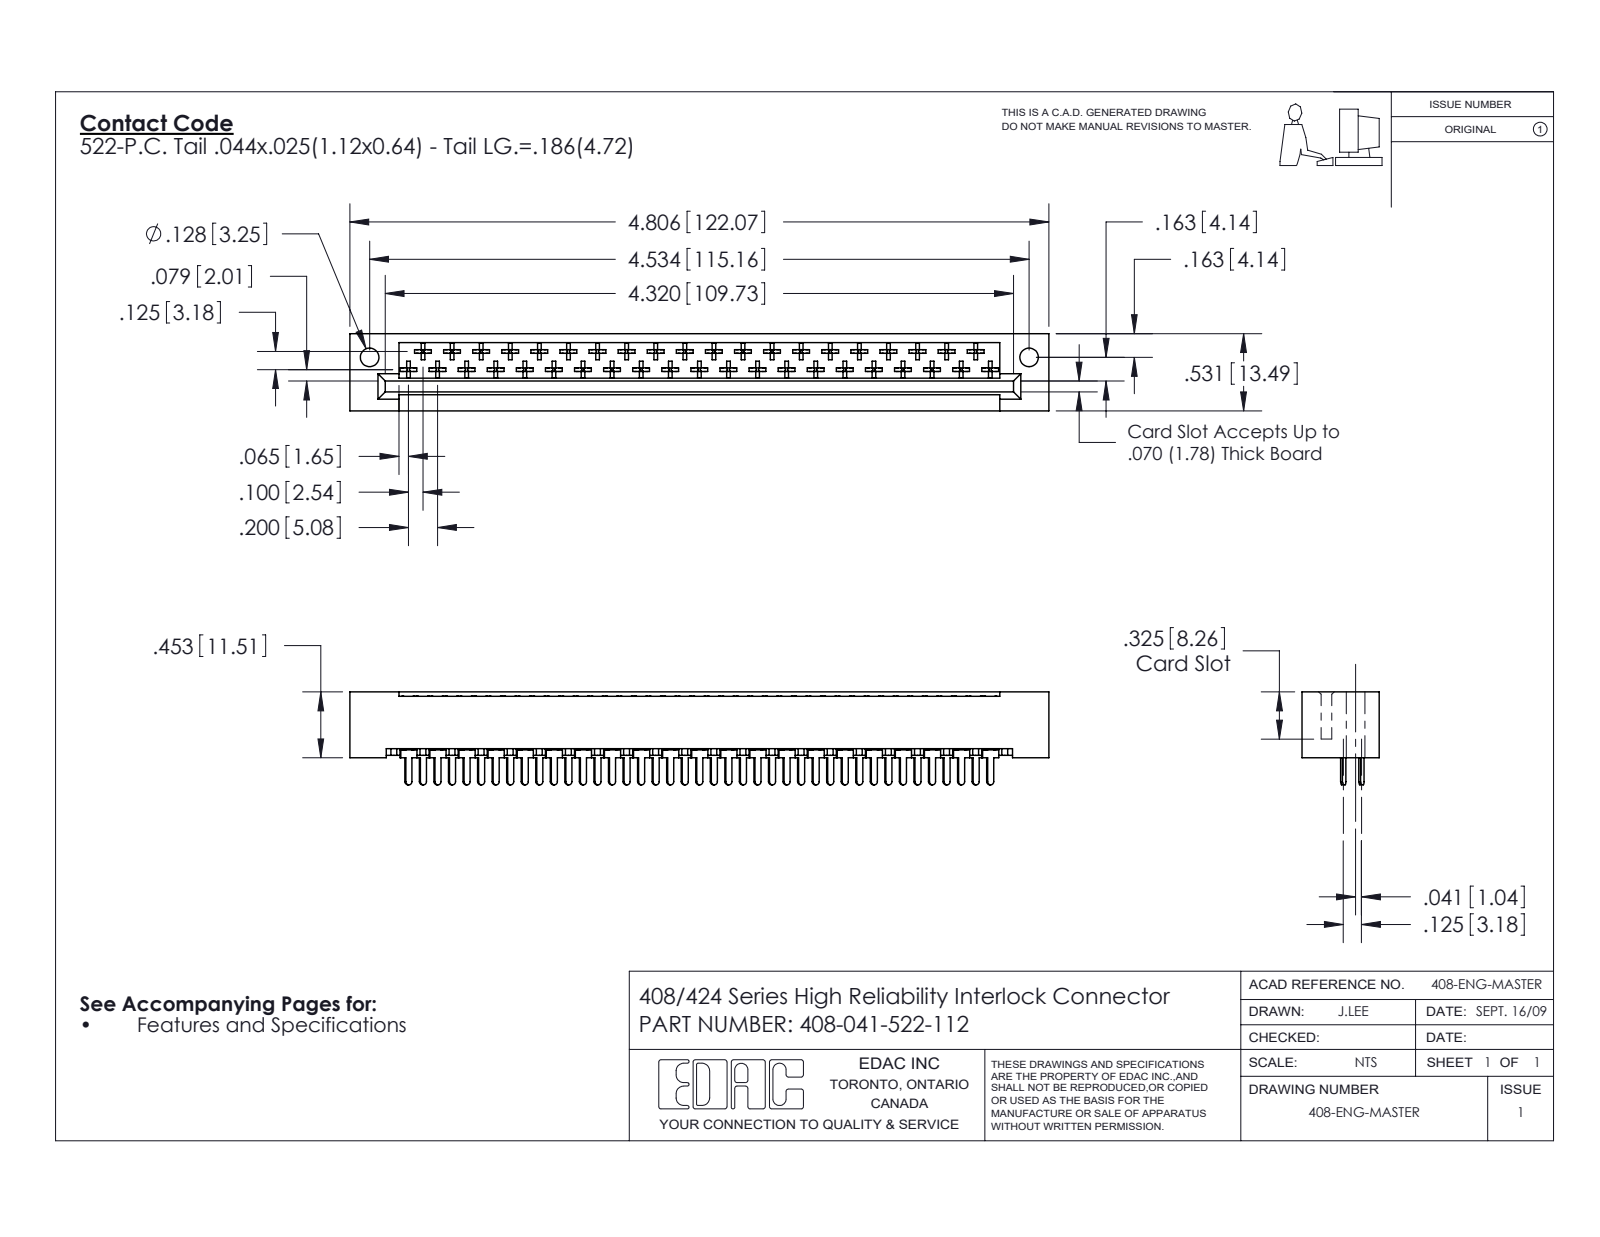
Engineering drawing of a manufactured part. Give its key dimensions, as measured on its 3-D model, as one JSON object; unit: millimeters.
{"part_name": "408 Part_041 - 1; 408-290-001_408-290-122; 408-047-522-112", "step_written_by": "SolidWorks 2016 (CONFIG_CONTROL_DESIGN)", "units": "millimeters", "bodies": {"solids": 42, "faces": 2299, "planar": 1758, "cylindrical": 377, "other": 164}, "overall_size": [122.1, 16.2, 13.5], "volume_mm3": 14000, "surface_area_mm2": 16810, "round_holes": [[3.3, 2]], "partial_cylinders_radius": [[0.3, 246], [0.5, 43], [0.6, 41]], "face_to_face_distances": [13.5, 2.5, 3.2, 0.6, 0.6, 10.2, 6.6, 6.9, 6, 7.5], "hole_center_spacings": [115.2]}
